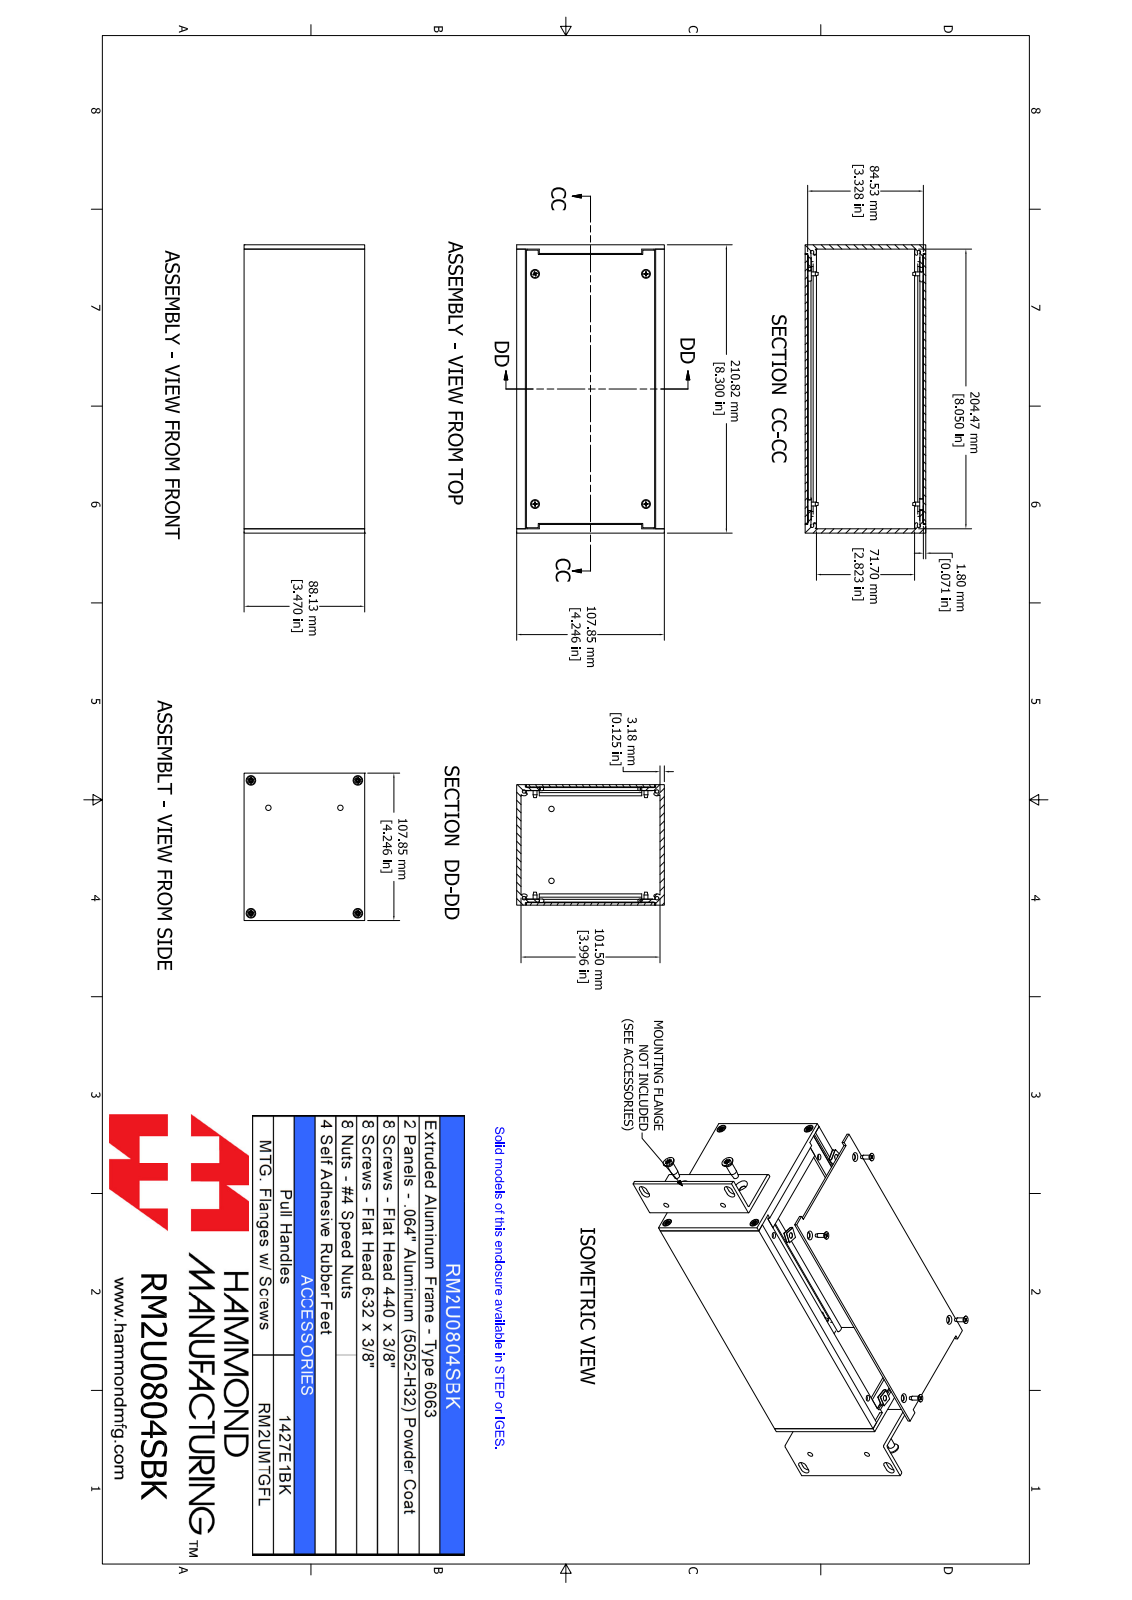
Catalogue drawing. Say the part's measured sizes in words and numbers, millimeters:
The part is named "RM2U0804SBK". Its 3-D file was written by "SolidWorks 2021 (AUTOMOTIVE_DESIGN)". It is 34 solids with 852 faces: 428 planar, 136 cylindrical and 288 other. Overall it measures 210.8 by 107.8 by 88.1 millimeters. Its volume is 291 700 cubic millimeters and its surface area 237 600 square millimeters. Round holes: 6 of diameter 2.5, 6 of diameter 4, 4 of diameter 3.5, 4 of diameter 4.3, 2 of diameter 4. Round bosses or shafts: 4 of diameter 6, 4 of diameter 5.4, 4 of diameter 3.5, 4 of diameter 2.8. Partial cylindrical surfaces (rounded edges, fillets, slot ends): 12 of radius 1, 12 of radius 1.2, 8 of radius 1.3, 8 of radius 3.2, 6 of radius 0.9, 5 of radius 1. The main face-to-face distances are 3.2, 1.8, 86.3, 104.7, 88.1, 107.8, 84.5, 101.5, 82.1, 4.2. The hole center spacings are 78.1, 78.2, 81.1, 88.5, 97.2, 101.1, 124.6, 168.3.
